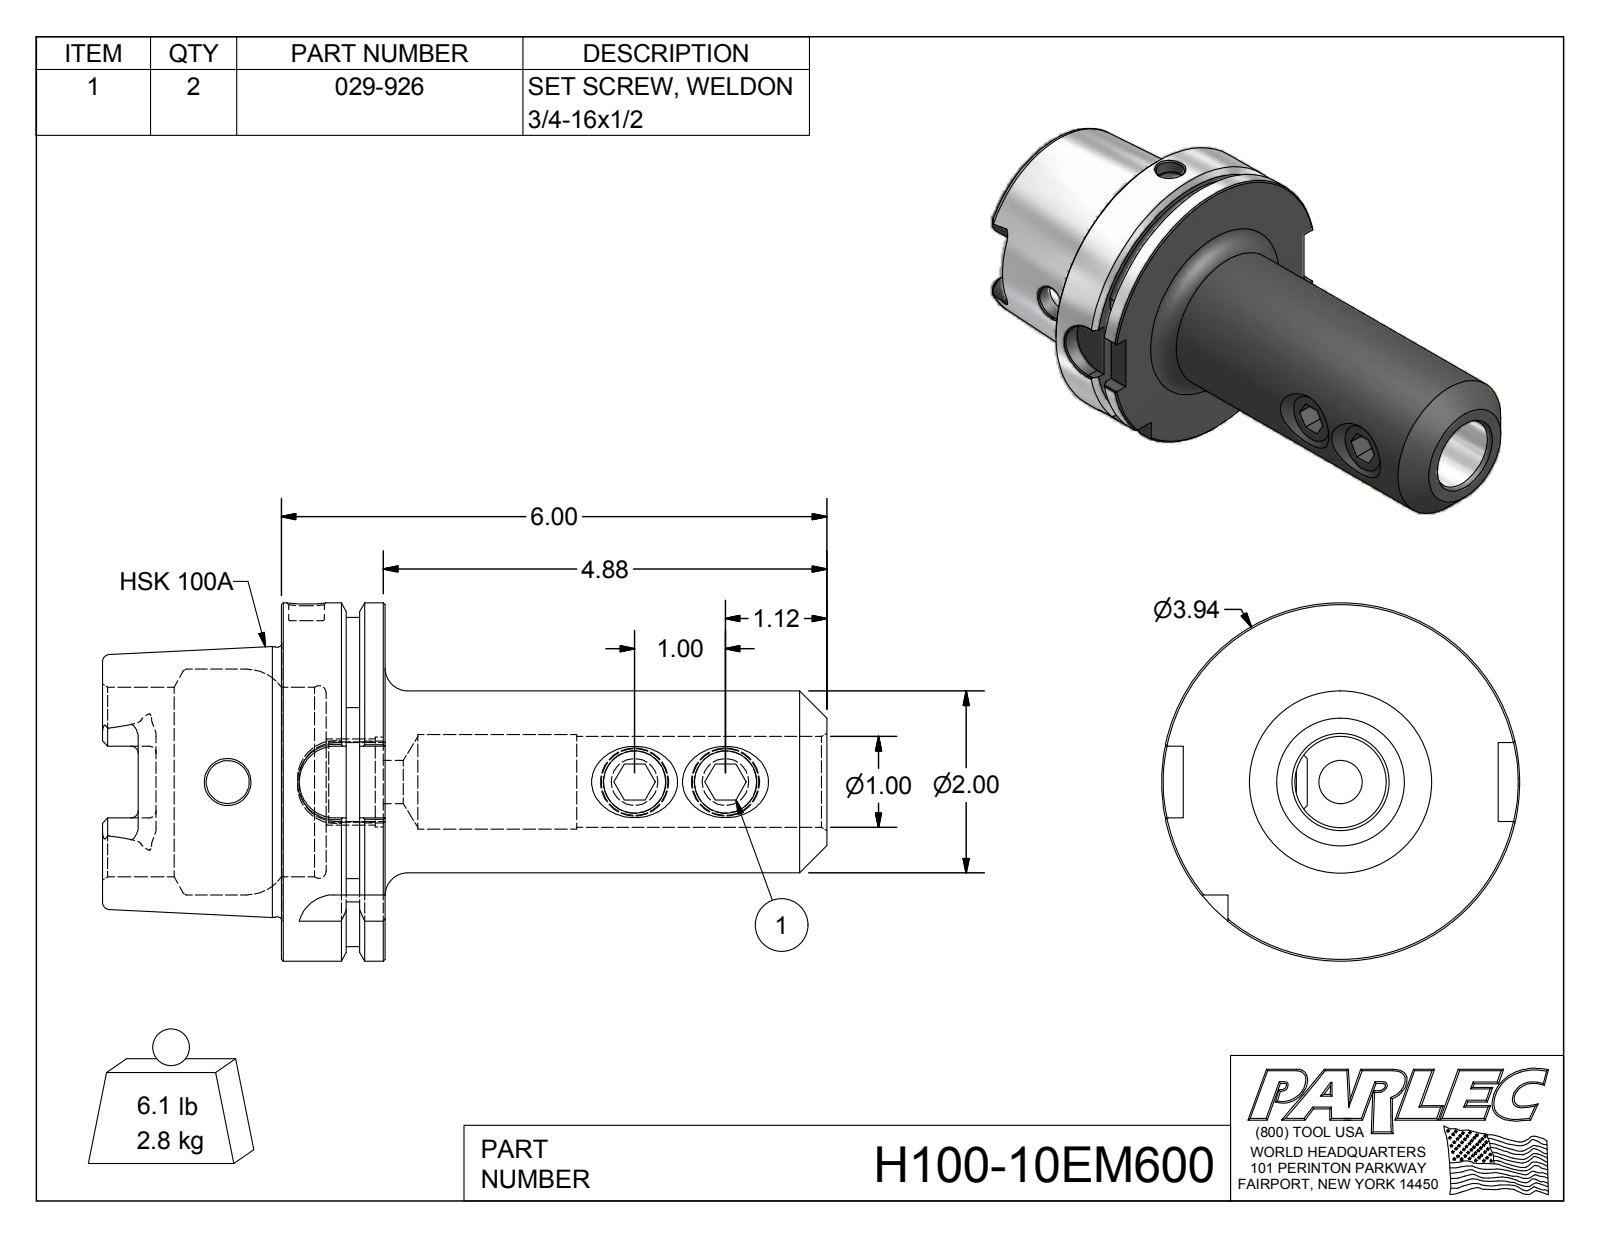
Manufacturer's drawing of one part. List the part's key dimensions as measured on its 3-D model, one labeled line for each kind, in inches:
Part name (STEP PRODUCT): H100-10EM600; 029-926
STEP written by: Autodesk Inventor 2012 (AUTOMOTIVE_DESIGN)
Units: inches
Bodies: 3 solids, 154 faces (62 planar, 38 cylindrical, 54 other)
Overall size (bounding box): 7.969 × 3.937 × 3.937
Volume: 26.71 in³ · Surface area: 126.3 in²
Round holes (diameter × count): ⌀0.472 ×2, ⌀0.682 ×2, ⌀0.394 ×1, ⌀0.881 ×1, ⌀0.985 ×1, ⌀1 ×1, ⌀1.04 ×1, ⌀2.087 ×1, ⌀2.48 ×1
Round bosses / shafts (diameter × count): ⌀0.75 ×2, ⌀3.937 ×1, ⌀2.967 ×1, ⌀2 ×1
Partial cylindrical surfaces — rounded edges, fillets, slot ends (radius × count): R0.079 ×6, R0.192 ×4, R0.394 ×4, R1.811 ×1
Main face-to-face distances: 1.142, 0.492, 0.65, 1.969, 2.461, 3.11, 0.394, 2.83, 0.861, 0.369
Hole centre spacings: 1, 4.476, 5.476
